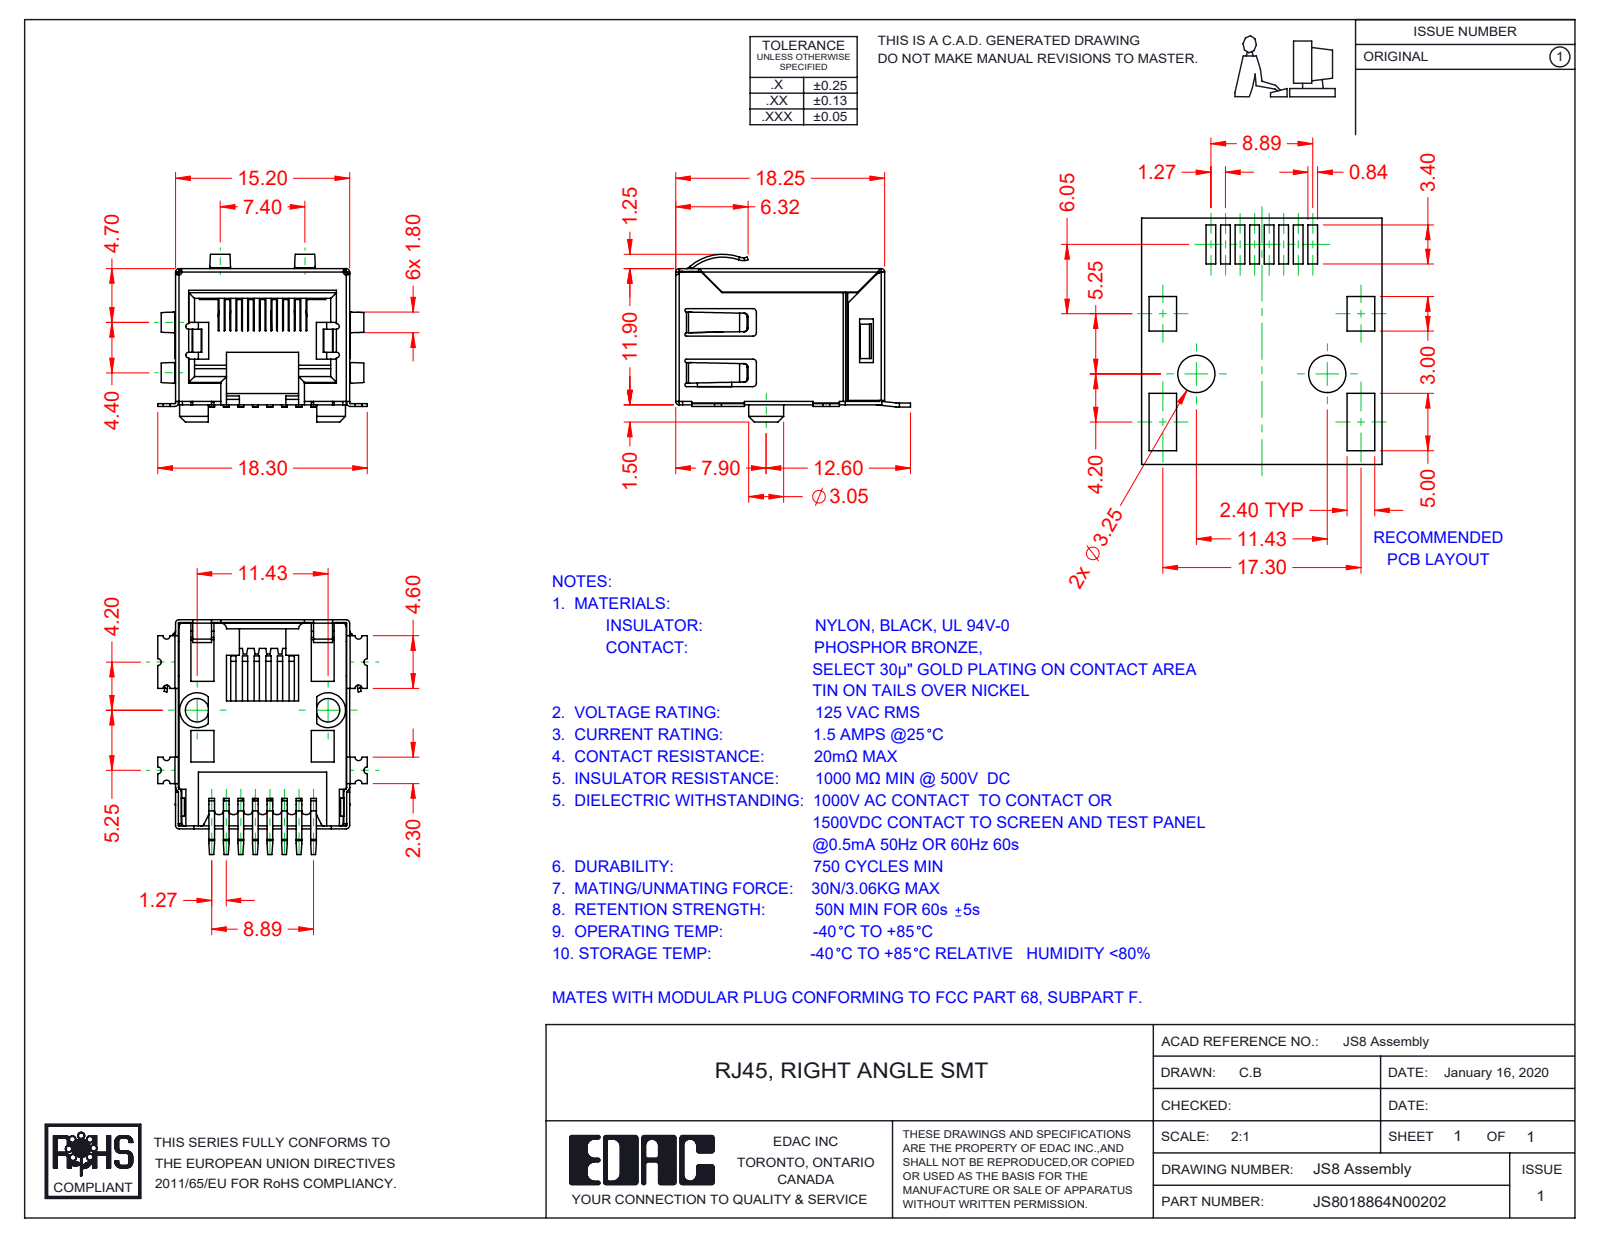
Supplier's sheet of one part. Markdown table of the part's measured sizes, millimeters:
| quantity | value |
| --- | --- |
| part name | RJS8018864N00202; S8 Contacts; S8 Shield; S8 Insulator |
| STEP written by | SolidWorks 2016 (CONFIG_CONTROL_DESIGN) |
| units | millimeters |
| bodies | 10 solids, 976 faces (602 planar, 314 cylindrical, 60 other) |
| overall size | 20.5 × 18.3 × 14.65 |
| volume | 1 308 mm³ |
| surface area | 4 634 mm² |
| partial cylindrical surfaces (radius × count) | 0.3 × 59, 0.25 × 19, 0.5 × 18, 0.2 × 17, 0.15 × 8, 0.75 × 7, 1 × 4, 1.25 × 3 |
| main face-to-face distances | 14.65, 14.95, 14.9, 1, 0.35, 14.7, 0.75, 10.9, 1.1, 15.2 |
